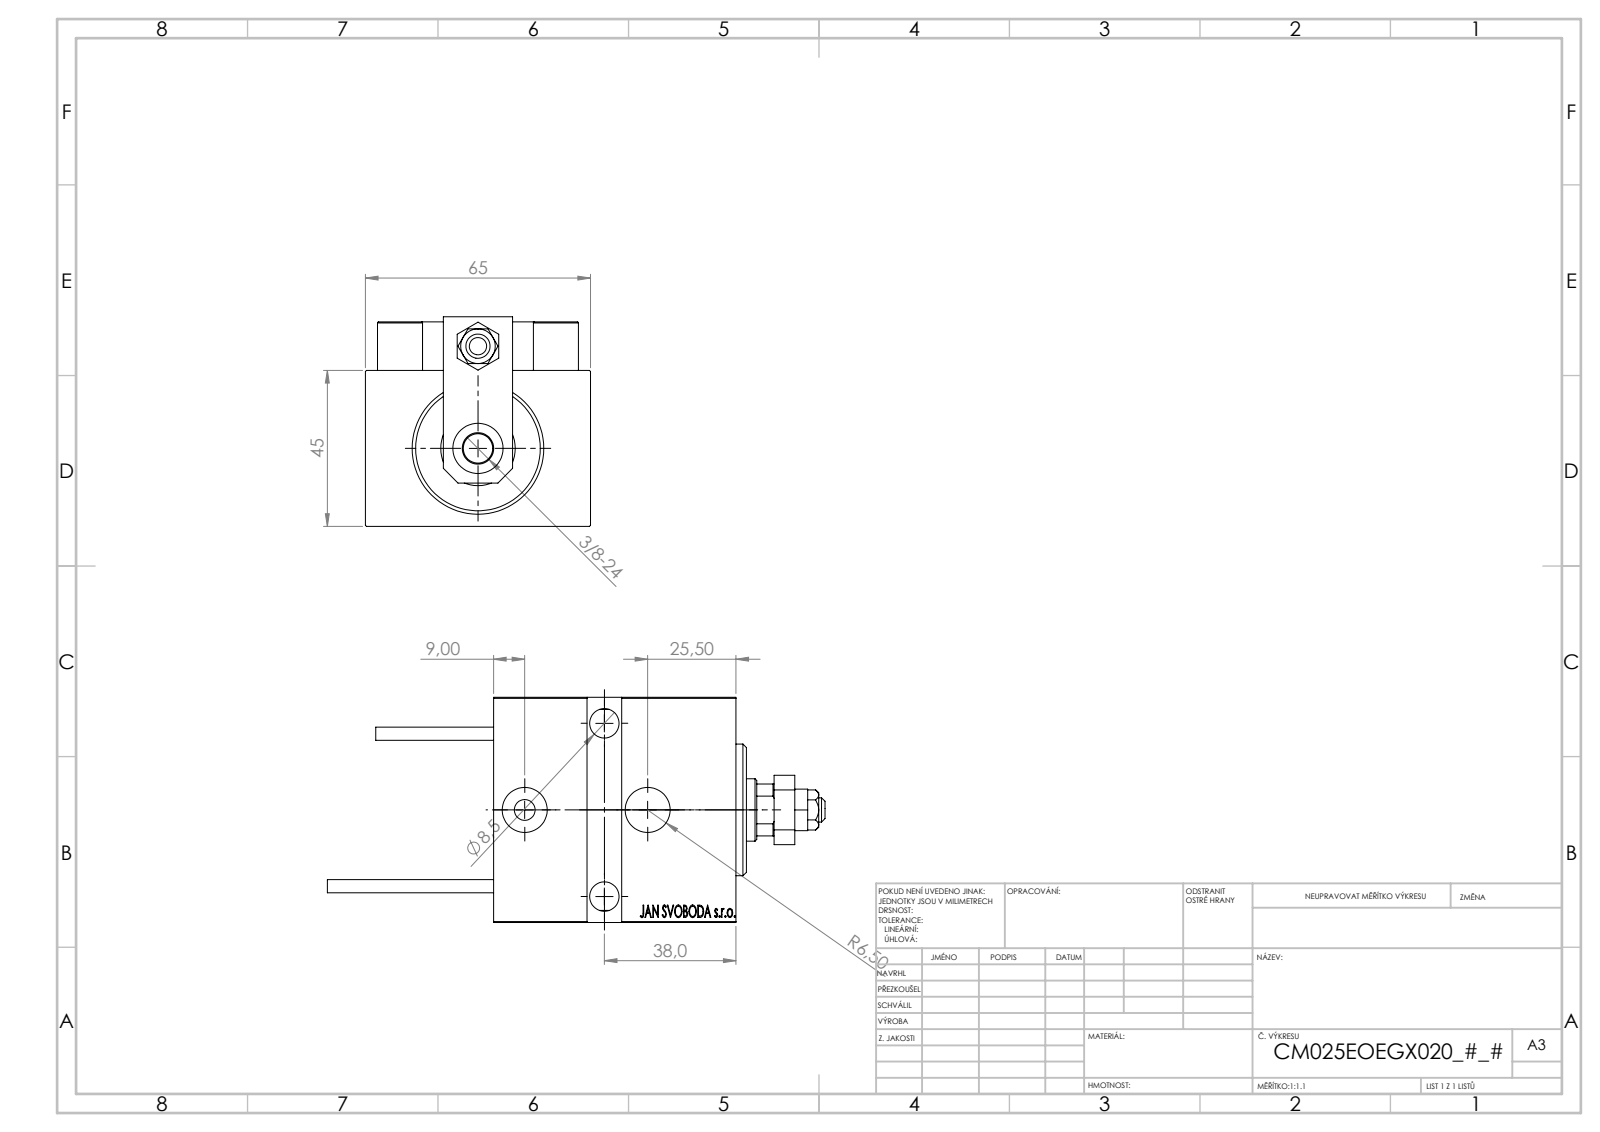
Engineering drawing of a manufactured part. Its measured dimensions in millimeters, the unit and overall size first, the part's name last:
Units: millimetres
Overall size (bounding box): 143.7 × 65 × 60.5
Round holes (diameter × count): ⌀8 ×5, ⌀3.2 ×4, ⌀4 ×4, ⌀8.5 ×3, ⌀5 ×2, ⌀13 ×2, ⌀13.5 ×2, ⌀7 ×1, ⌀14.5 ×1, ⌀18 ×1, ⌀21.5 ×1, ⌀25 ×1
Round bosses / shafts (diameter × count): ⌀5 ×2, ⌀3.8 ×2, ⌀38 ×1, ⌀27 ×1, ⌀13 ×1, ⌀11 ×1, ⌀6 ×1
Partial cylindrical surfaces — rounded edges, fillets, slot ends (radius × count): R0.3 ×30, R3 ×2, R8.5 ×1
Main face-to-face distances: 45, 65, 14, 59, 6, 19, 8, 70, 58, 13
Hole centre spacings: 10.77, 11.37, 20, 21.03, 22.09, 27.95, 29.59, 29.69
Volume: 240 199 mm³ · Surface area: 62 347 mm²
Bodies: 24 solids, 1276 faces (567 planar, 168 cylindrical, 541 other)
Part name (STEP PRODUCT): Block; MAGNET; KONCOVKA; V450CM_E_VCP (+7 more)
STEP written by: SolidWorks 2019 (CONFIG_CONTROL_DESIGN)
